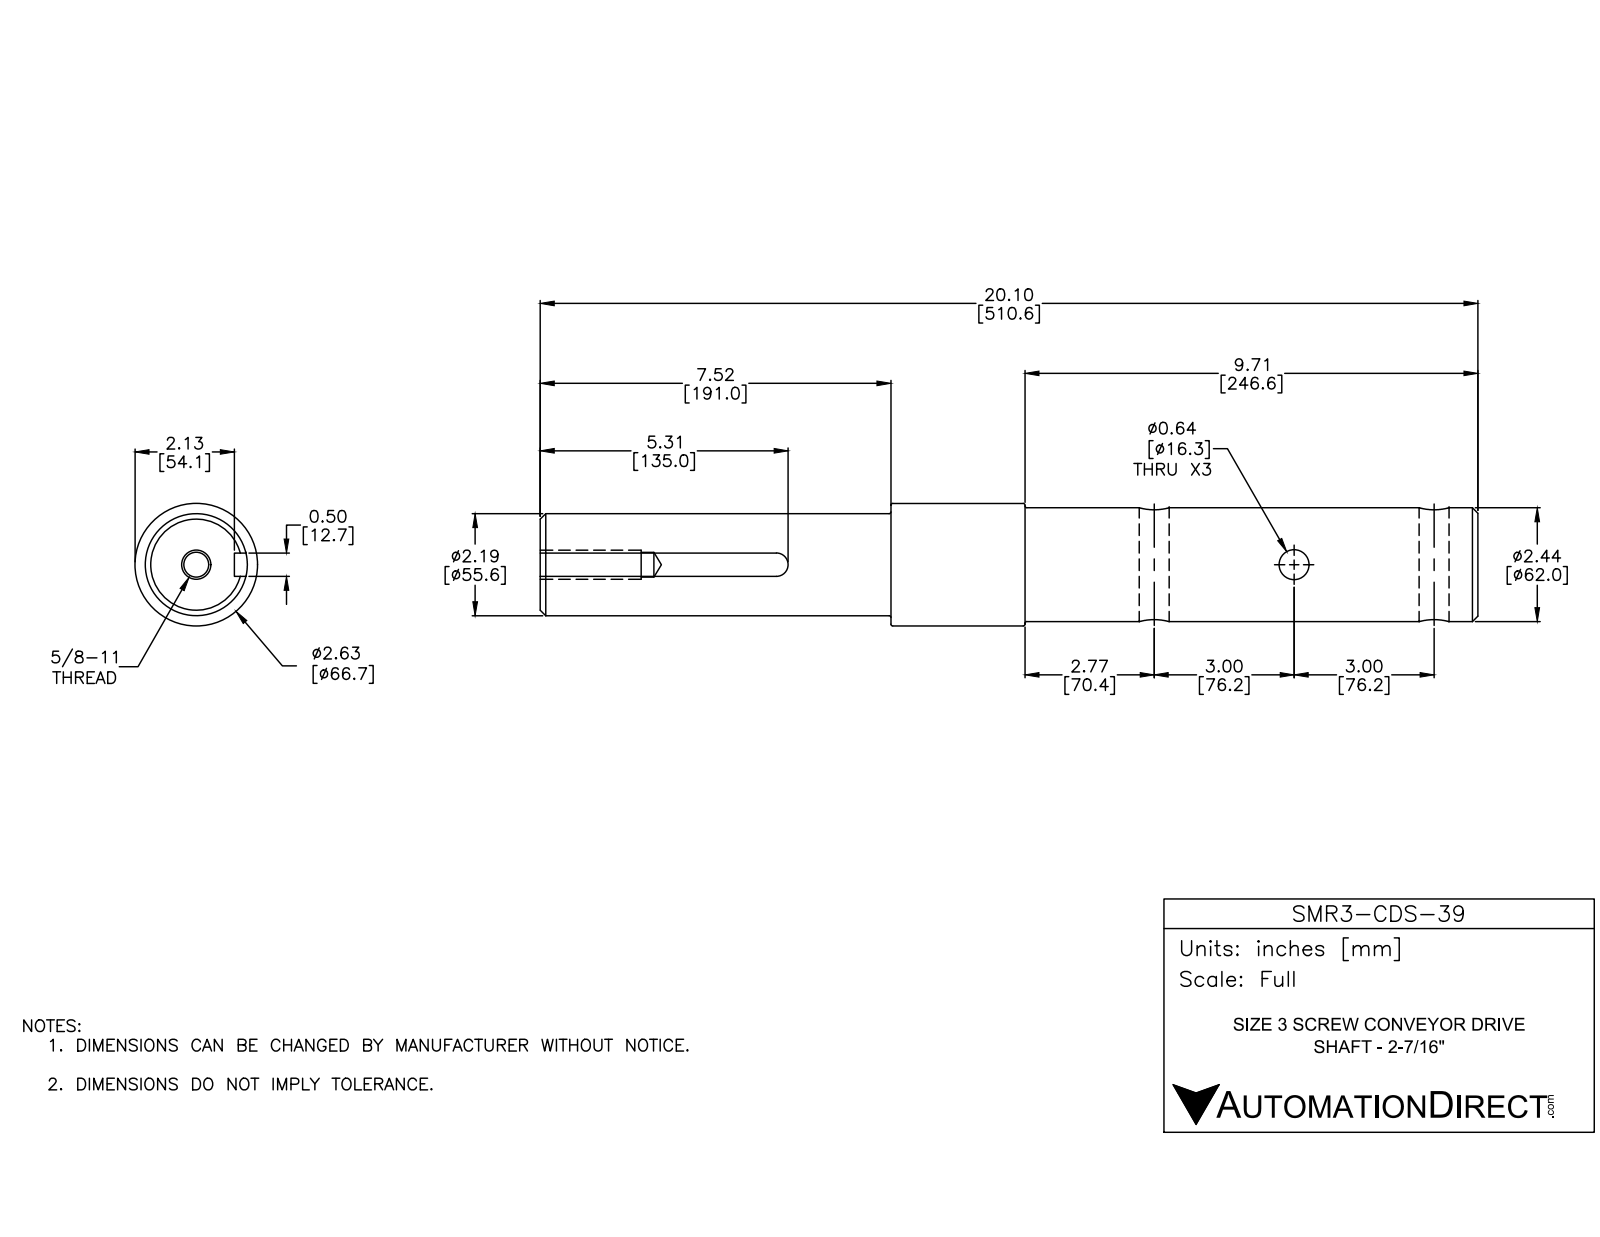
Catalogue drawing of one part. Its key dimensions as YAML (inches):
part_name: "SMR3-CDS-39"
step_written_by: "SolidWorks 2016 (AUTOMOTIVE_DESIGN)"
units: inches
bodies: {solids: 1, faces: 40, planar: 8, cylindrical: 18, other: 14}
overall_size: [20.103, 2.625, 2.625]
volume: 85.33
surface_area: 178.9
round_holes:
  - {diameter: 0.642, count: 3}
  - {diameter: 0.531, count: 1}
  - {diameter: 0.625, count: 1}
round_bosses_or_shafts:
  - {diameter: 2.625, count: 1}
  - {diameter: 2.44, count: 1}
  - {diameter: 2.187, count: 1}
partial_cylinders:
  - {radius: 0.25, count: 1}
face_to_face_distances: [20.104, 0.5, 7.52, 12.584, 10.394, 2.874, 9.71, 2.165, 5.354, 8.228]
hole_center_spacings: [6]
